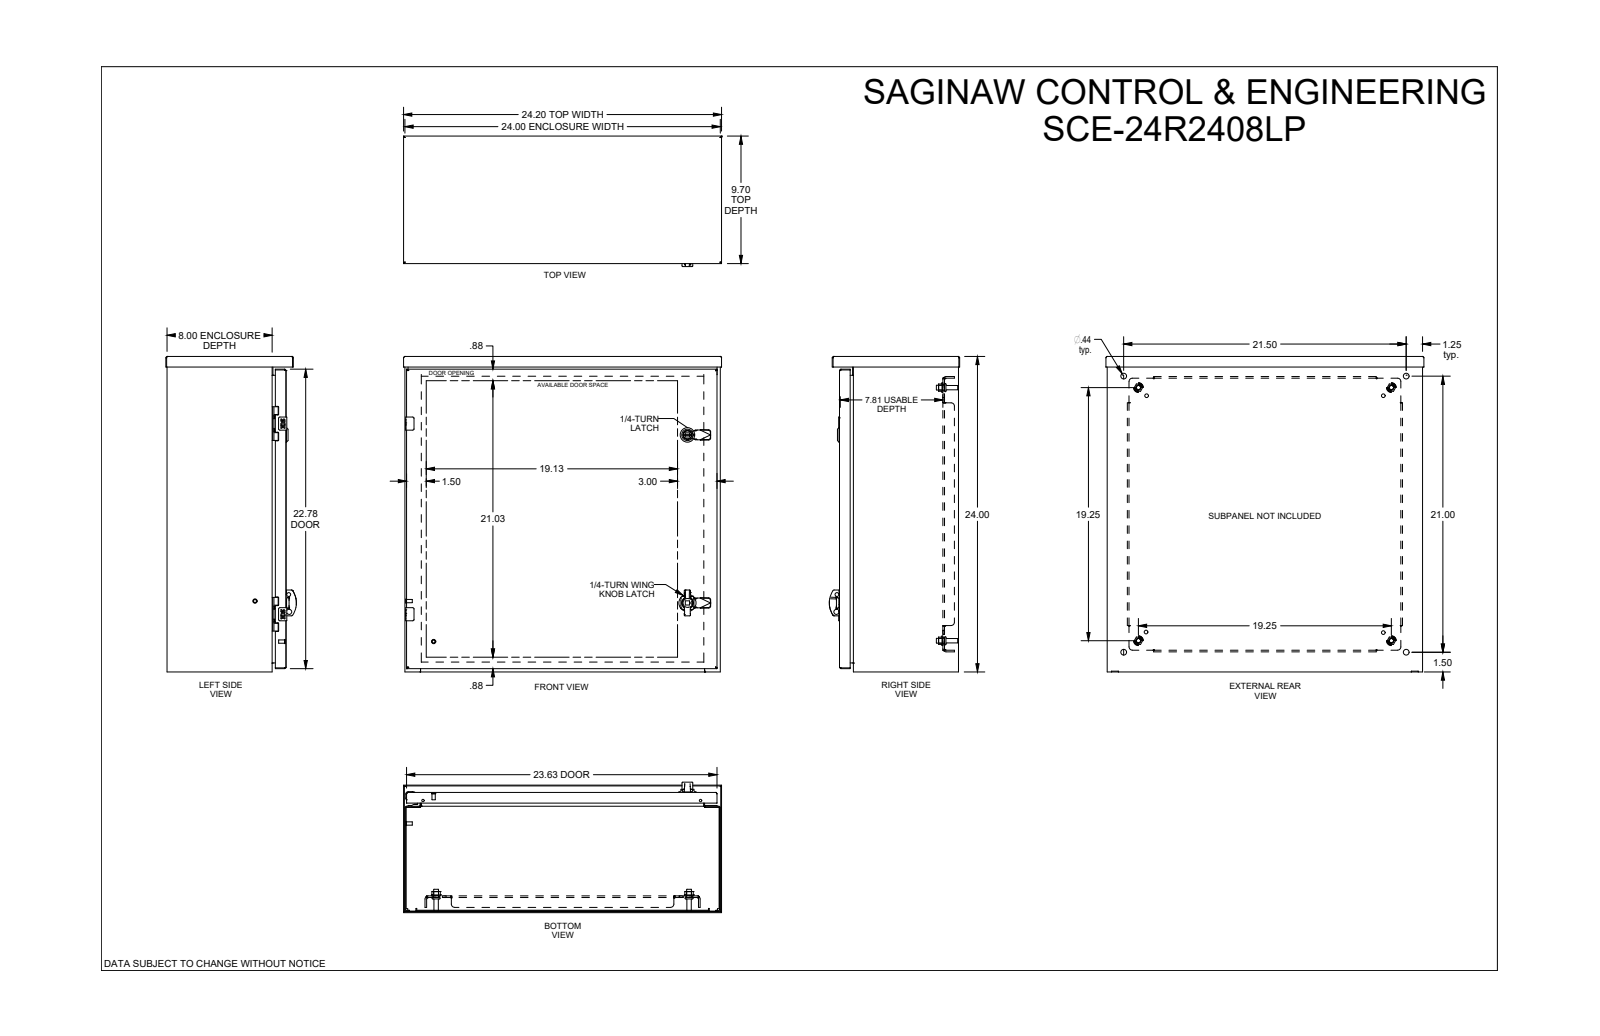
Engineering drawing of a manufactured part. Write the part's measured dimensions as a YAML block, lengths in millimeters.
part_name: "SCE-24R2408LP"
step_written_by: "SolidWorks 2019 (CONFIG_CONTROL_DESIGN)"
units: millimeters
bodies: {solids: 0, faces: 2429, planar: 1160, cylindrical: 823, other: 446}
overall_size: [614.7, 609.6, 252.1]
round_holes:
  - {diameter: 4.4, count: 4}
  - {diameter: 5.2, count: 4}
  - {diameter: 6.2, count: 4}
  - {diameter: 6.8, count: 4}
  - {diameter: 7.1, count: 4}
  - {diameter: 9.3, count: 4}
  - {diameter: 9.5, count: 4}
  - {diameter: 11.1, count: 4}
  - {diameter: 12.7, count: 4}
  - {diameter: 1, count: 2}
  - {diameter: 4, count: 2}
  - {diameter: 5.5, count: 2}
round_bosses_or_shafts:
  - {diameter: 4.3, count: 6}
  - {diameter: 9.3, count: 4}
  - {diameter: 8.4, count: 4}
  - {diameter: 6.4, count: 4}
  - {diameter: 6.1, count: 4}
  - {diameter: 5, count: 3}
  - {diameter: 22, count: 2}
  - {diameter: 20.4, count: 2}
partial_cylinders:
  - {radius: 0.4, count: 72}
  - {radius: 0.3, count: 60}
  - {radius: 0.3, count: 26}
  - {radius: 0.5, count: 24}
  - {radius: 2.8, count: 23}
  - {radius: 1.5, count: 22}
  - {radius: 1.3, count: 19}
  - {radius: 0.8, count: 15}
face_to_face_distances: [1.5, 608.1, 1.5, 226.9, 228.4, 229.9, 228.4, 3.2, 25.4, 201.5]
hole_center_spacings: [368.3, 0.6, 12.5, 25, 473.5, 518, 727.4, 22.2]
